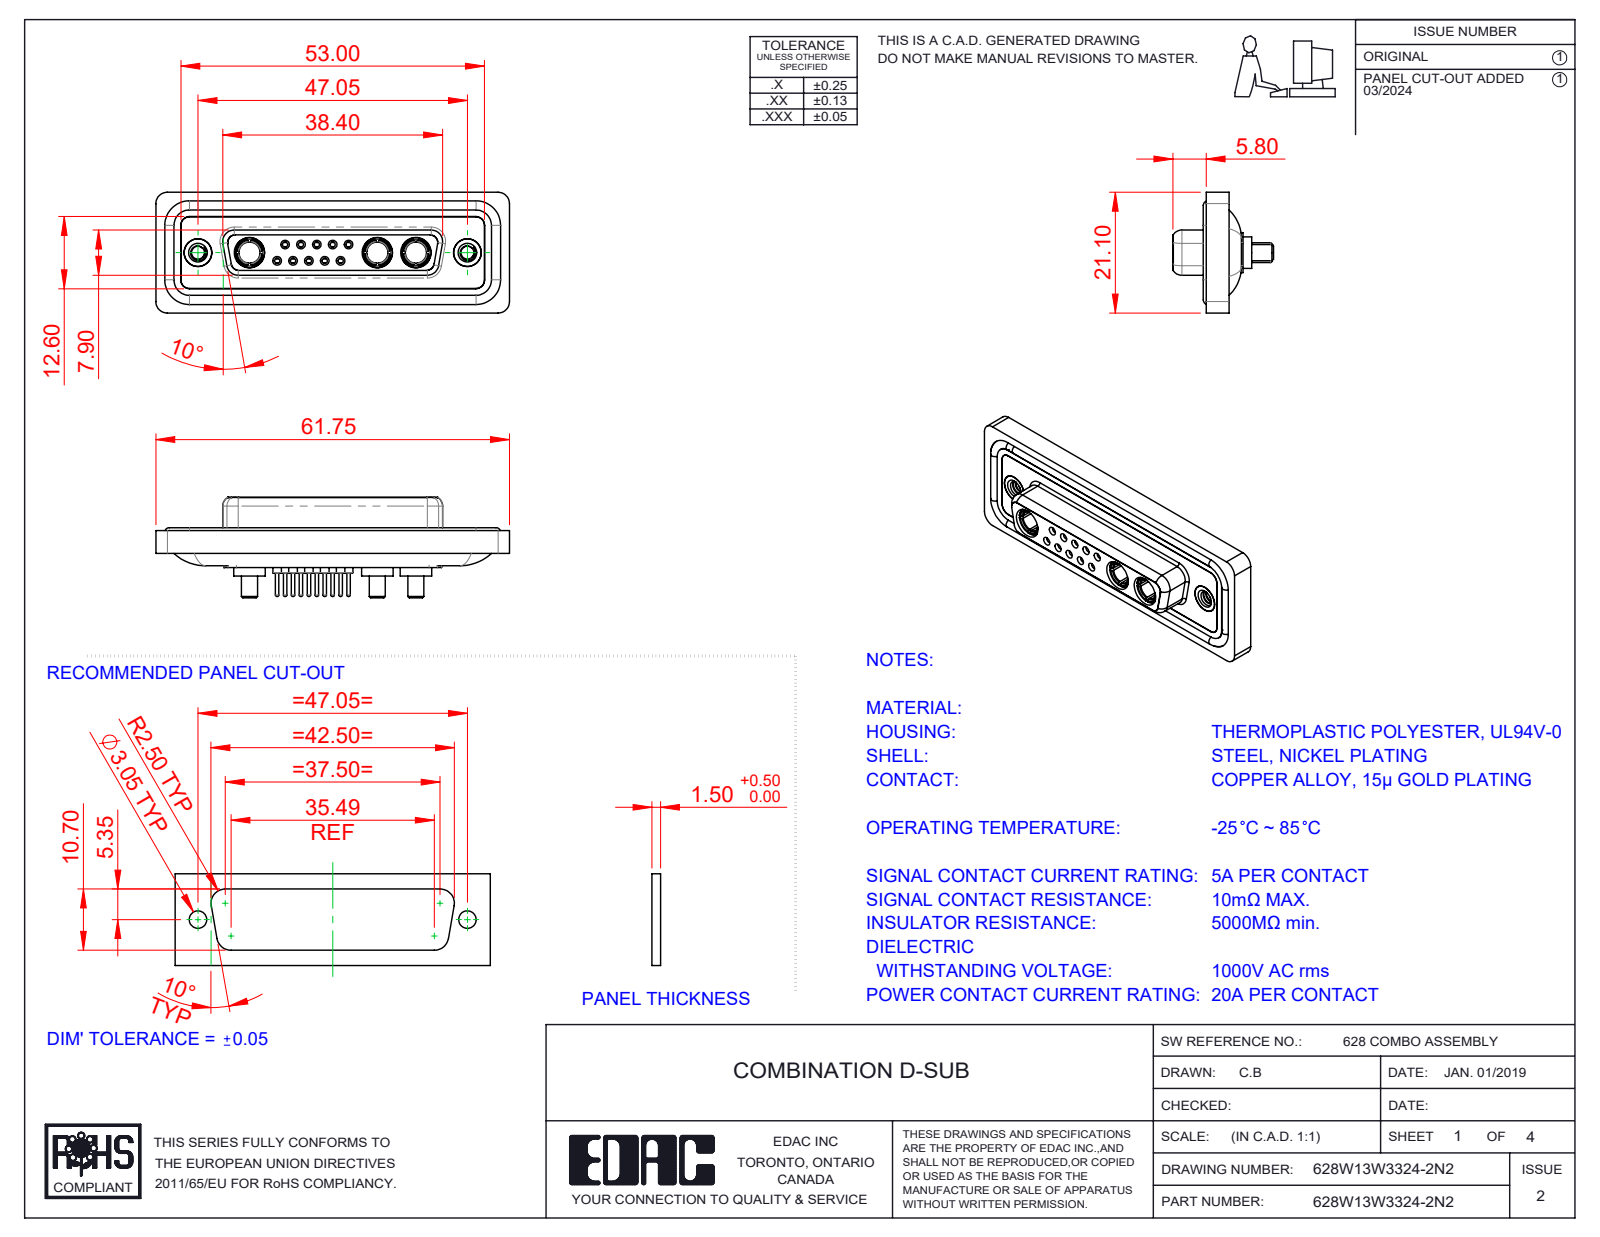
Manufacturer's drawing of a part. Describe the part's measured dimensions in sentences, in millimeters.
The part is named "628Combo Contact Row 2_24; 628Combo Housing_13W3; 628Combo Threaded Rivet_2; Power Socket_20A S (+5 more)". Its 3-D file was written by "SolidWorks 2023 (CONFIG_CONTROL_DESIGN)". It is 23 solids with 1158 faces: 342 planar, 447 cylindrical and 369 other. Overall it measures 61.75 by 21.1 by 17.55 millimeters. Its volume is 8 273 cubic millimeters and its surface area 13 709 square millimeters. Round holes: 10 of diameter 0.9, 10 of diameter 1.1, 10 of diameter 1.5, 10 of diameter 2, 5 of diameter 1.6, 5 of diameter 1.7, 5 of diameter 4.85, 3 of diameter 3.7, 3 of diameter 5.3, 2 of diameter 2.26, 2 of diameter 4, 2 of diameter 4.05. Round bosses or shafts: 10 of diameter 2.2, 10 of diameter 0.6, 9 of diameter 1.6, 3 of diameter 5.5, 3 of diameter 5.2, 3 of diameter 4.96, 3 of diameter 4.75, 3 of diameter 3.75. Partial cylindrical surfaces (rounded edges, fillets, slot ends): 22 of radius 1.5, 18 of radius 2, 8 of radius 1.35, 8 of radius 1.6, 4 of radius 0.25, 4 of radius 0.5, 4 of radius 0.6, 4 of radius 0.65. The main face-to-face distances are 0.4, 1.8, 7.45, 5.65, 0.5, 6.6, 7.05, 1.6, 2.9, 1.1. The hole center spacings are 3.16, 2.77, 5.03, 5.04, 5.54, 8.31, 7.49, 2.76.
